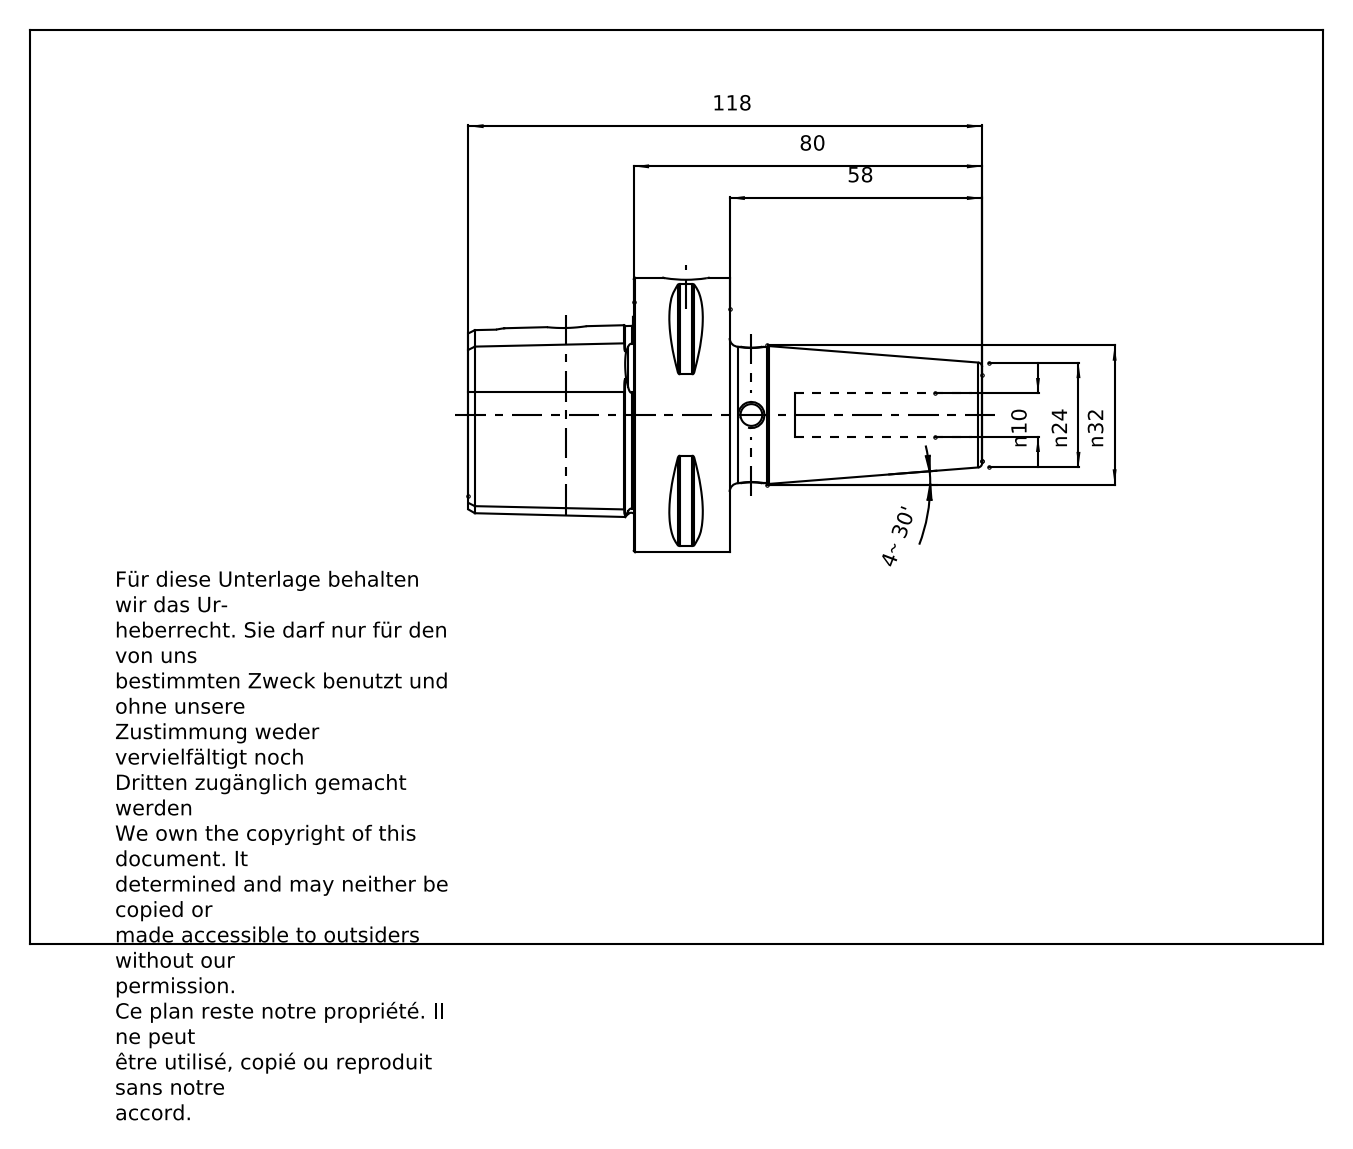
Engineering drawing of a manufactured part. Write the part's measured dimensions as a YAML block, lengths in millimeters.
part_name: "CC6-140-10"
step_written_by: "PRO/ENGINEER BY PARAMETRIC TECHNOLOGY CORPORATION, 2010430 (CONFIG_CONTROL_DESIGN)"
units: millimeters
bodies: {solids: 1, faces: 120, planar: 23, cylindrical: 33, other: 64}
overall_size: [118, 63, 63]
volume: 129366
surface_area: 27515
round_holes:
  - {diameter: 4.25, count: 1}
  - {diameter: 8.1, count: 1}
  - {diameter: 10, count: 1}
  - {diameter: 10.04, count: 1}
  - {diameter: 18, count: 1}
  - {diameter: 28.02, count: 1}
  - {diameter: 32, count: 1}
round_bosses_or_shafts:
  - {diameter: 63, count: 1}
  - {diameter: 20, count: 1}
partial_cylinders:
  - {radius: 0.5, count: 8}
  - {radius: 6, count: 1}
face_to_face_distances: [22, 38, 60, 118, 80, 58, 24.88, 27, 11, 33]
hole_center_spacings: [27.5]
